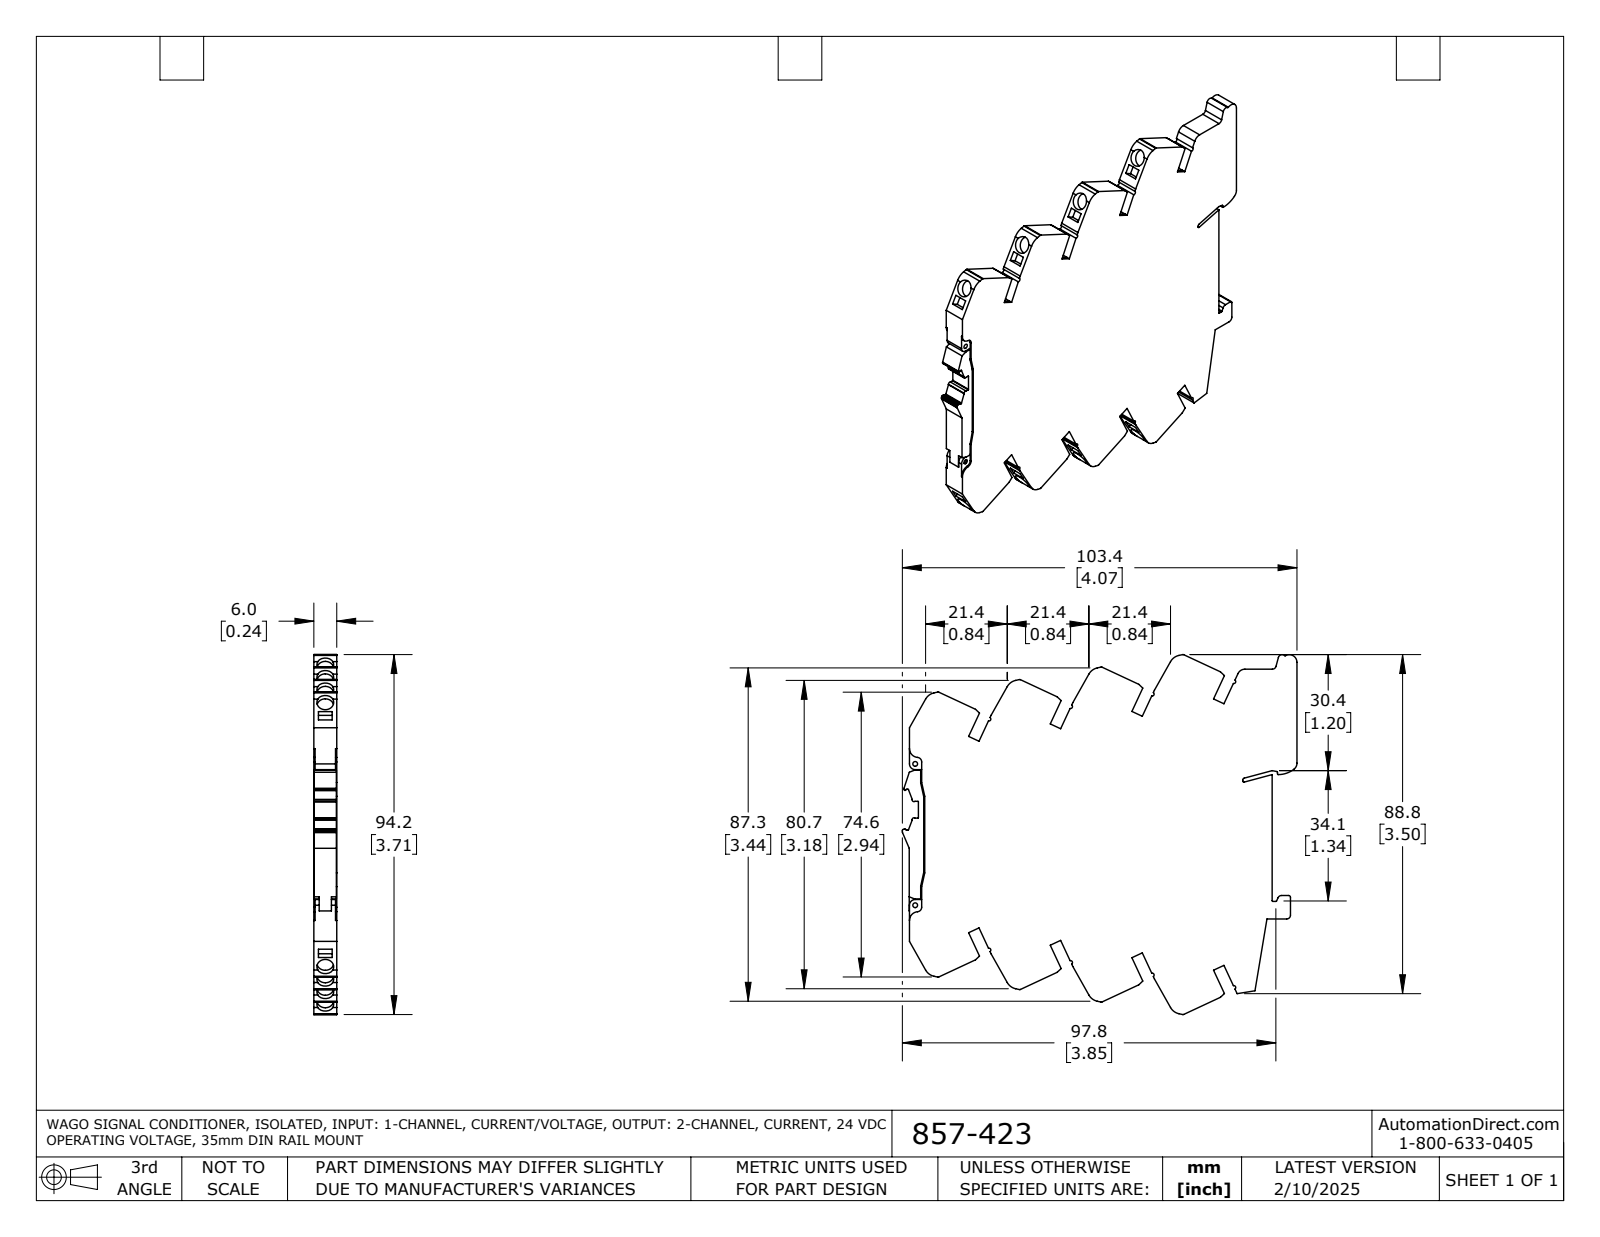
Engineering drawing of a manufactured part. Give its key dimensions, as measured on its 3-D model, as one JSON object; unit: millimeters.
{"part_name": "857-423", "step_written_by": "SolidWorks 2021 (AUTOMOTIVE_DESIGN)", "units": "millimeters", "bodies": {"solids": 1, "faces": 317, "planar": 219, "cylindrical": 98, "other": 0}, "overall_size": [103.4, 94.3, 6], "volume_mm3": 43930, "surface_area_mm2": 19260, "round_holes": [[4.4, 8], [1.2, 2]], "partial_cylinders_radius": [[0.5, 12], [0.2, 11], [0.4, 8], [3.4, 8], [1, 4], [0.3, 3], [2, 3], [0.5, 2]], "face_to_face_distances": [6, 18, 17, 12, 5.9, 12, 3, 24, 36, 6.5], "hole_center_spacings": [13.4, 13.3, 26.7, 26.7, 26.7, 37, 40, 40.1]}
